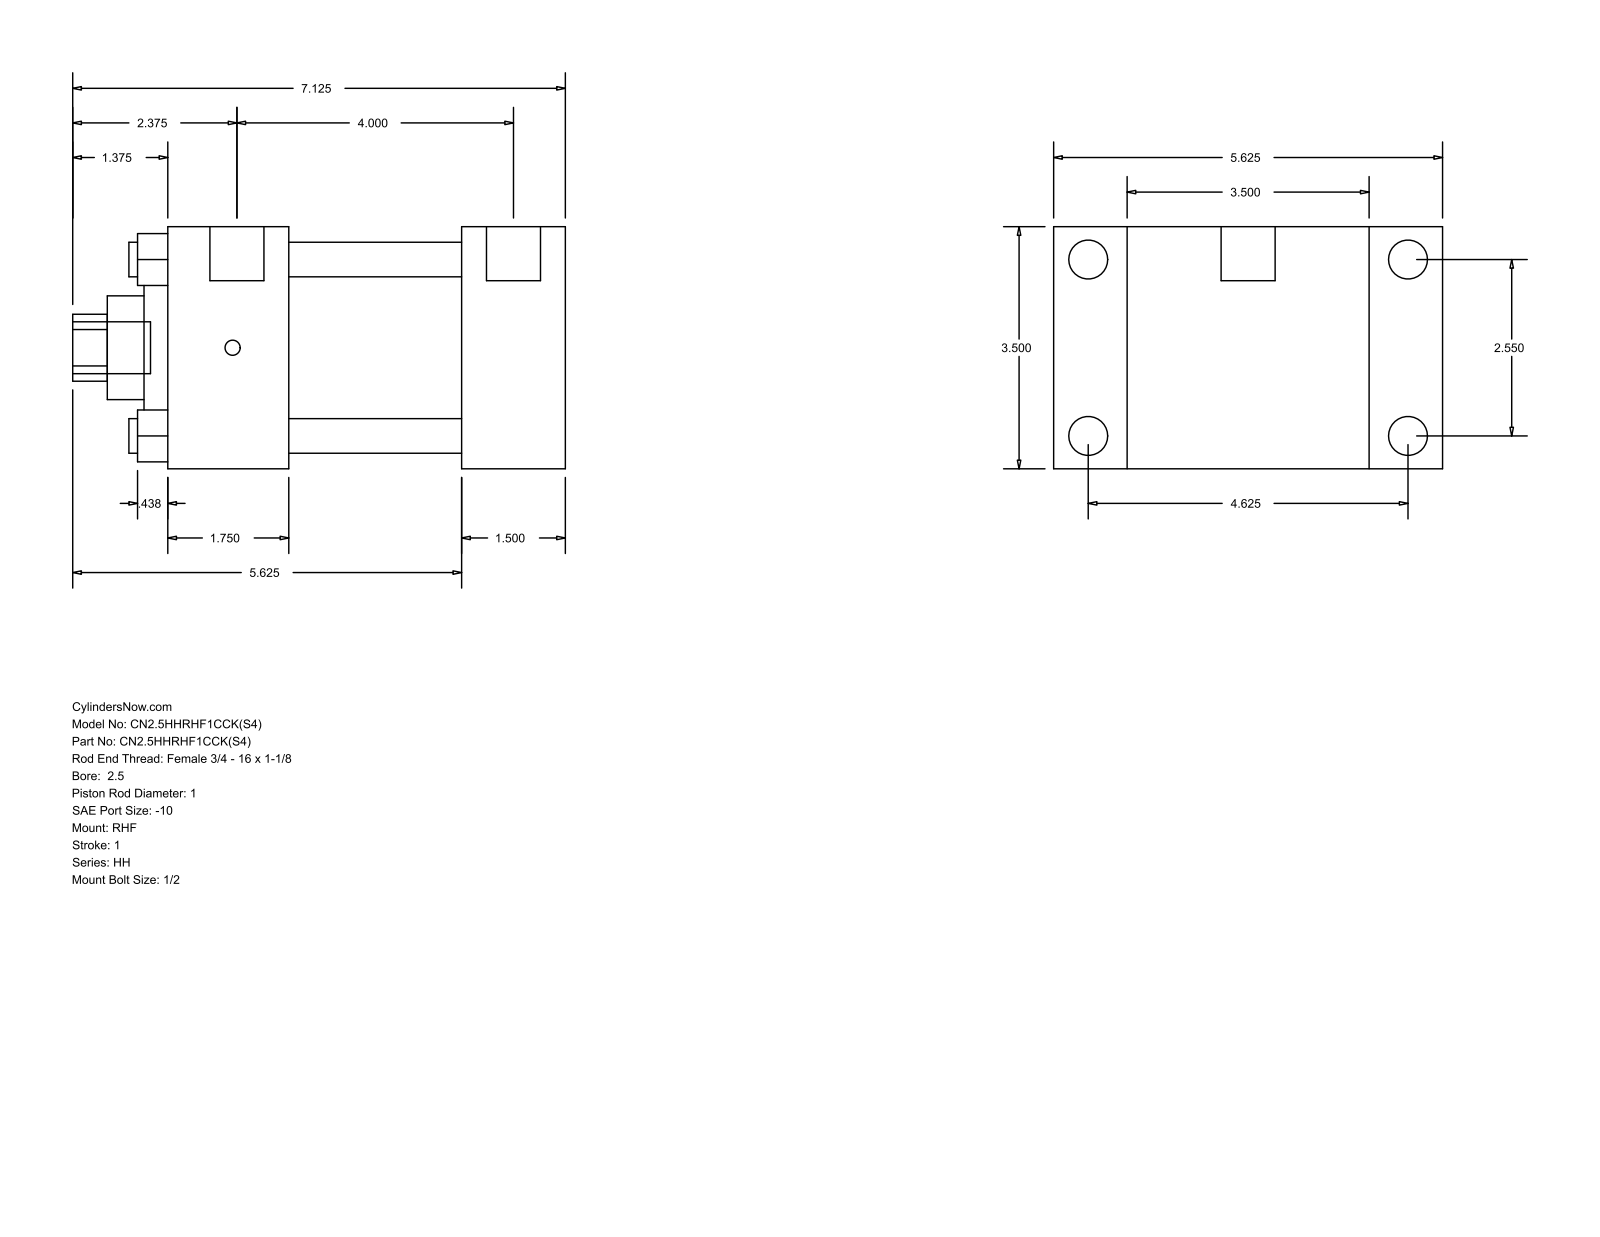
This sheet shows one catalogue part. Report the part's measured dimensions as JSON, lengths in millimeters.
{"part_name": "HH_RHF__0250_1", "step_written_by": "GSSL Pune (CONFIG_CONTROL_DESIGN)", "units": "millimeters", "bodies": {"solids": 0, "faces": 90, "planar": 61, "cylindrical": 29, "other": 0}, "overall_size": [180.97, 142.88, 88.9], "round_holes": [[12.7, 4], [25.4, 1], [38.1, 1], [60.33, 1], [73.03, 1]], "round_bosses_or_shafts": [[14.3, 4], [5.56, 4], [19.84, 2], [19.05, 1]], "partial_cylinders_radius": [[12.29, 1]], "face_to_face_distances": [88.9, 38.09, 26.99, 115.89, 107.96, 146.05, 142.88, 44.46, 63.5, 101.59], "hole_center_spacings": [45.79, 64.76, 91.58]}
